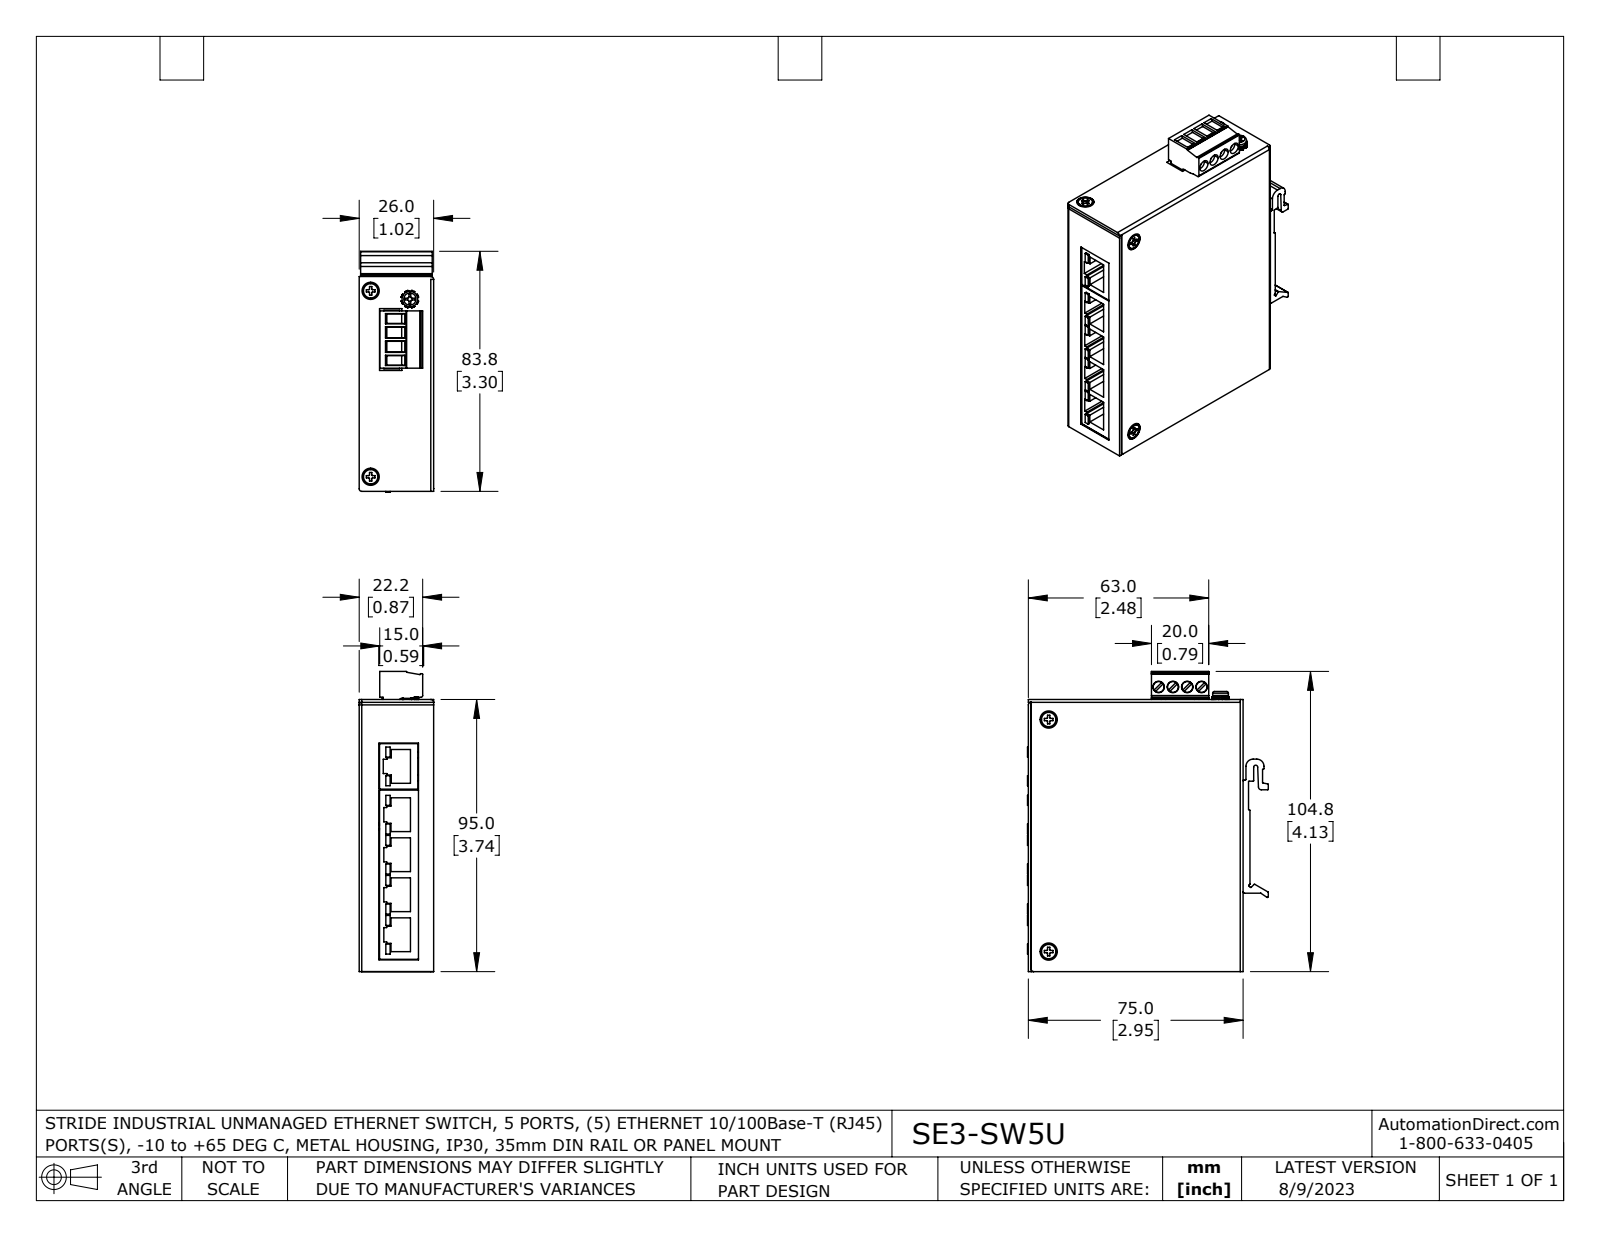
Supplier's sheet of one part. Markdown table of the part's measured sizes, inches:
| quantity | value |
| --- | --- |
| part name | LEONTON_CET2-0500_3D red1 ext1 AA coord fxt sr1 |
| STEP written by | SolidWorks 2021 (AUTOMOTIVE_DESIGN) |
| units | inches |
| bodies | 18 solids, 1330 faces (709 planar, 441 cylindrical, 180 other) |
| overall size | 4.126 × 3.311 × 1.024 |
| volume | 2.853 in³ |
| surface area | 93.64 in² |
| round holes (diameter × count) | 0.157 × 7, 0.236 × 6, 0.079 × 4, 0.096 × 4, 0.097 × 2, 0.097 × 2, 0.059 × 1, 0.091 × 1 |
| round bosses / shafts (diameter × count) | 0.197 × 9, 0.118 × 9, 0.165 × 4, 0.157 × 4, 0.149 × 4, 0.149 × 4, 0.217 × 1, 0.114 × 1 |
| partial cylindrical surfaces (radius × count) | 0.01 × 52, 0.004 × 47, 0.008 × 33, 0.008 × 10, 0.02 × 9, 0.039 × 7, 0.035 × 5, 0.011 × 4 |
| main face-to-face distances | 0.039, 0.934, 0.973, 0.02, 0.984, 1.024, 0.05, 3.701, 1.004, 0.031 |
| hole center spacings | 0.394, 0.406, 0.197, 2.953, 0.419, 0.726, 1.193, 1.4 |
